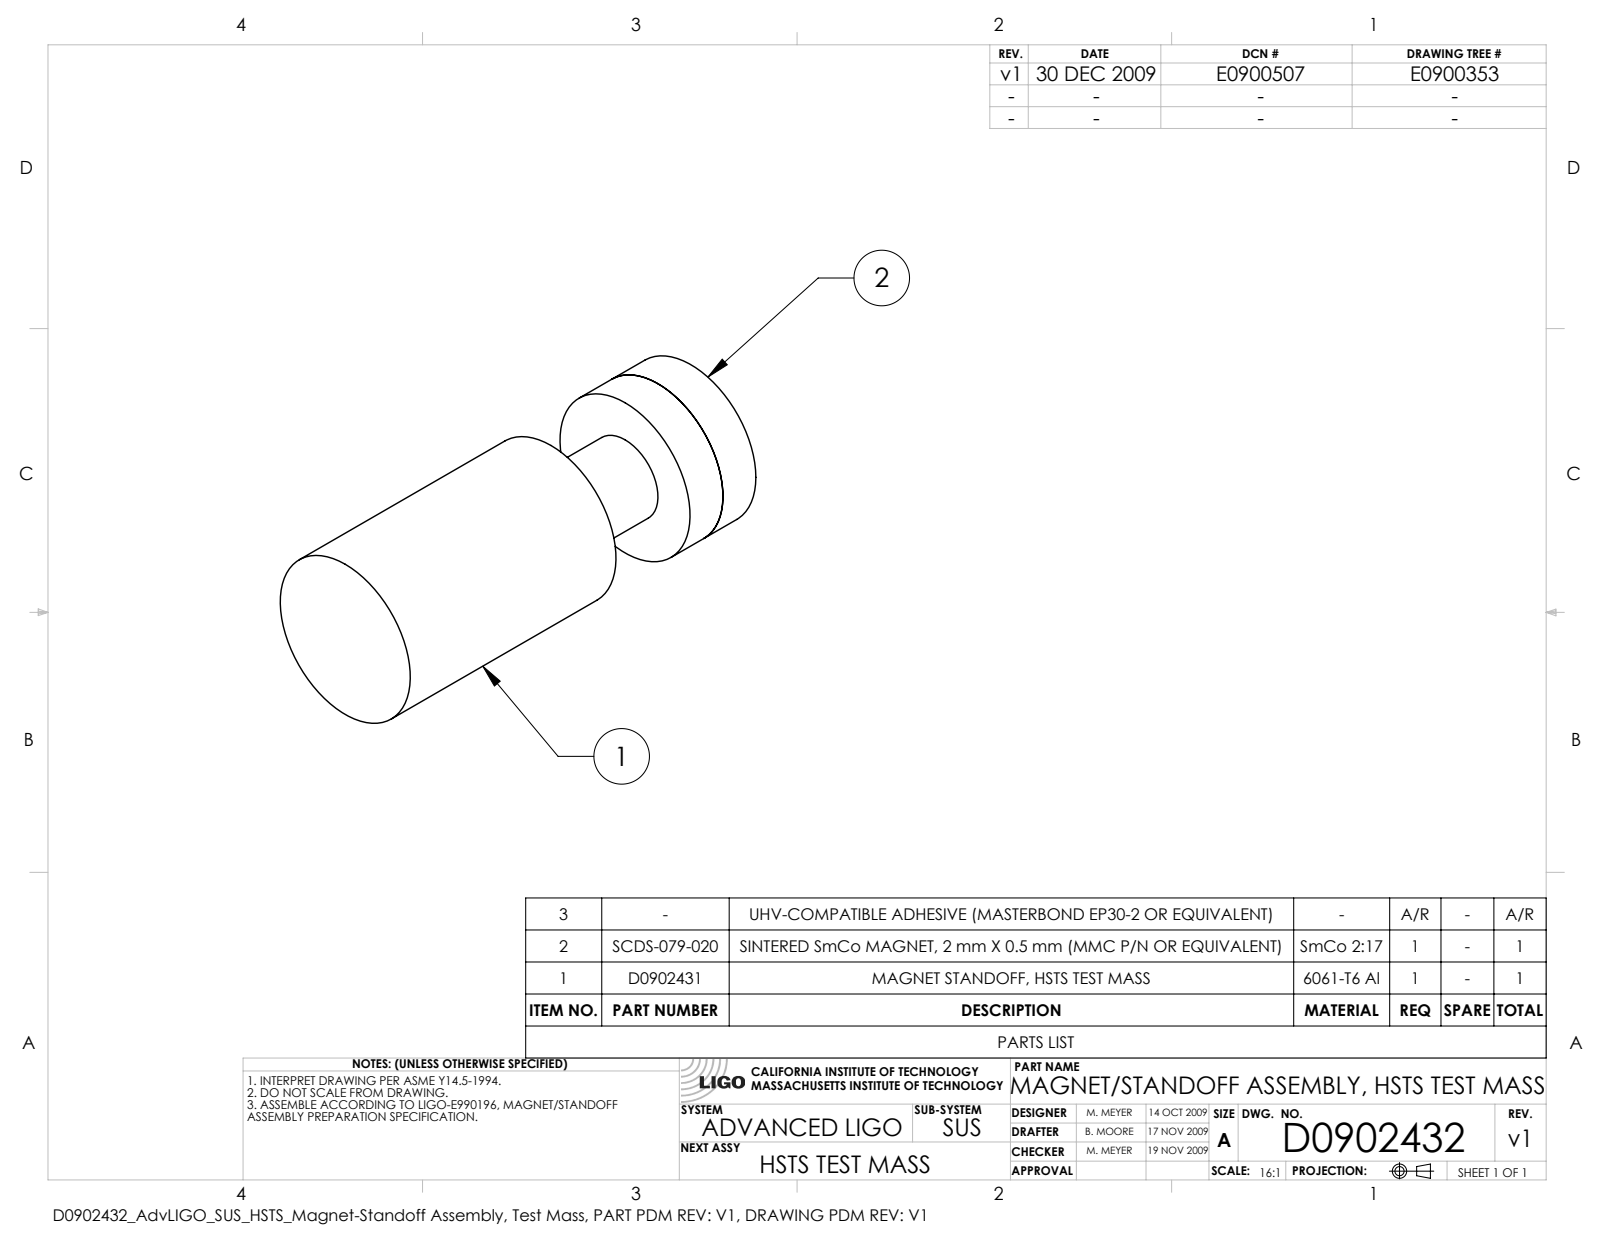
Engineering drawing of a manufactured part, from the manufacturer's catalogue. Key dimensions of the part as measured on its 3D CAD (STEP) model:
Part name (STEP PRODUCT): D0902431_AdvLIGO_SUS_HSTS_Magnet Standoff, Test Mass; D0902432-v1_aLIGO_SUS_HSTS_Magnet-Standoff Assembly, Test Mass; D0900040_Magnet,_MMC_SCDS-079-020; UHV-Compatible_Adhesive
STEP written by: SolidWorks 2009 (CONFIG_CONTROL_DESIGN)
Units: inches
Bodies: 2 solids, 14 faces (6 planar, 8 cylindrical, 0 other)
Overall size (bounding box): 0.21 × 0.079 × 0.079
Volume: 0.001 in³ · Surface area: 0.074 in²
Round bosses / shafts (diameter × count): ⌀0.079 ×1, ⌀0.04 ×1
Main face-to-face distances: 0.02, 0.19, 0.21, 0.04, 0.17, 0.085, 0.065, 0.045, 0.125
